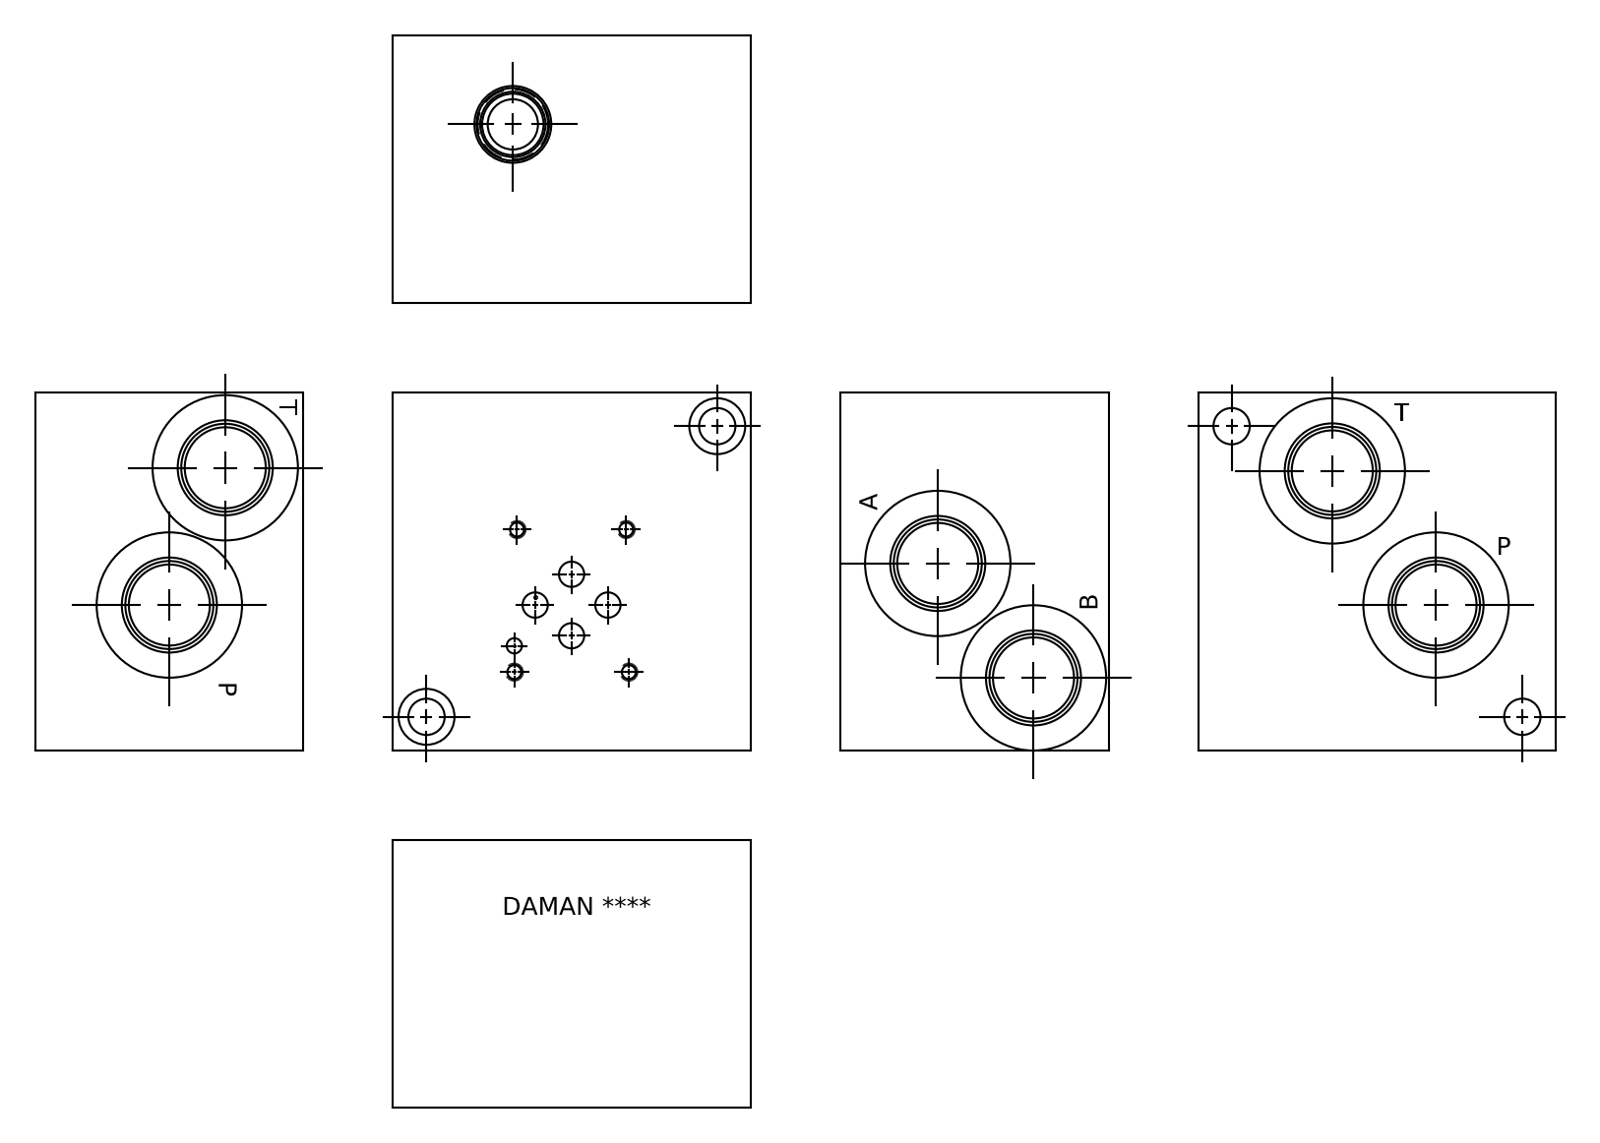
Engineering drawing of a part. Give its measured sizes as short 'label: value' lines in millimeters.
name: Part_AD03SPRVS12S.C10947_3D
written by: Autodesk Inventor 2019 (AUTOMOTIVE_DESIGN)
unit: mm
bodies: 1 solid, 570 faces (327 planar, 54 cylindrical, 189 other)
size: 101.6 × 101.6 × 76.2
volume: 643 250 mm³; area: 76 219 mm²
holes: 6× ⌀24.92, 6× ⌀27.43, 6× ⌀42.04, 5× ⌀23.01, 4× ⌀3.78, 4× ⌀4.83, 3× ⌀7.14, 3× ⌀26.99, 3× ⌀27, 2× ⌀7.92, 2× ⌀10.31, 2× ⌀15.88
face distances: 101.6, 76.2, 0.79, 100.81, 4.85, 71.35, 100.02, 19.05, 19.84, 81.76
hole spacings: 13.52, 13.54, 22.05, 33.55, 40.5, 51.45, 58.93, 6.4
